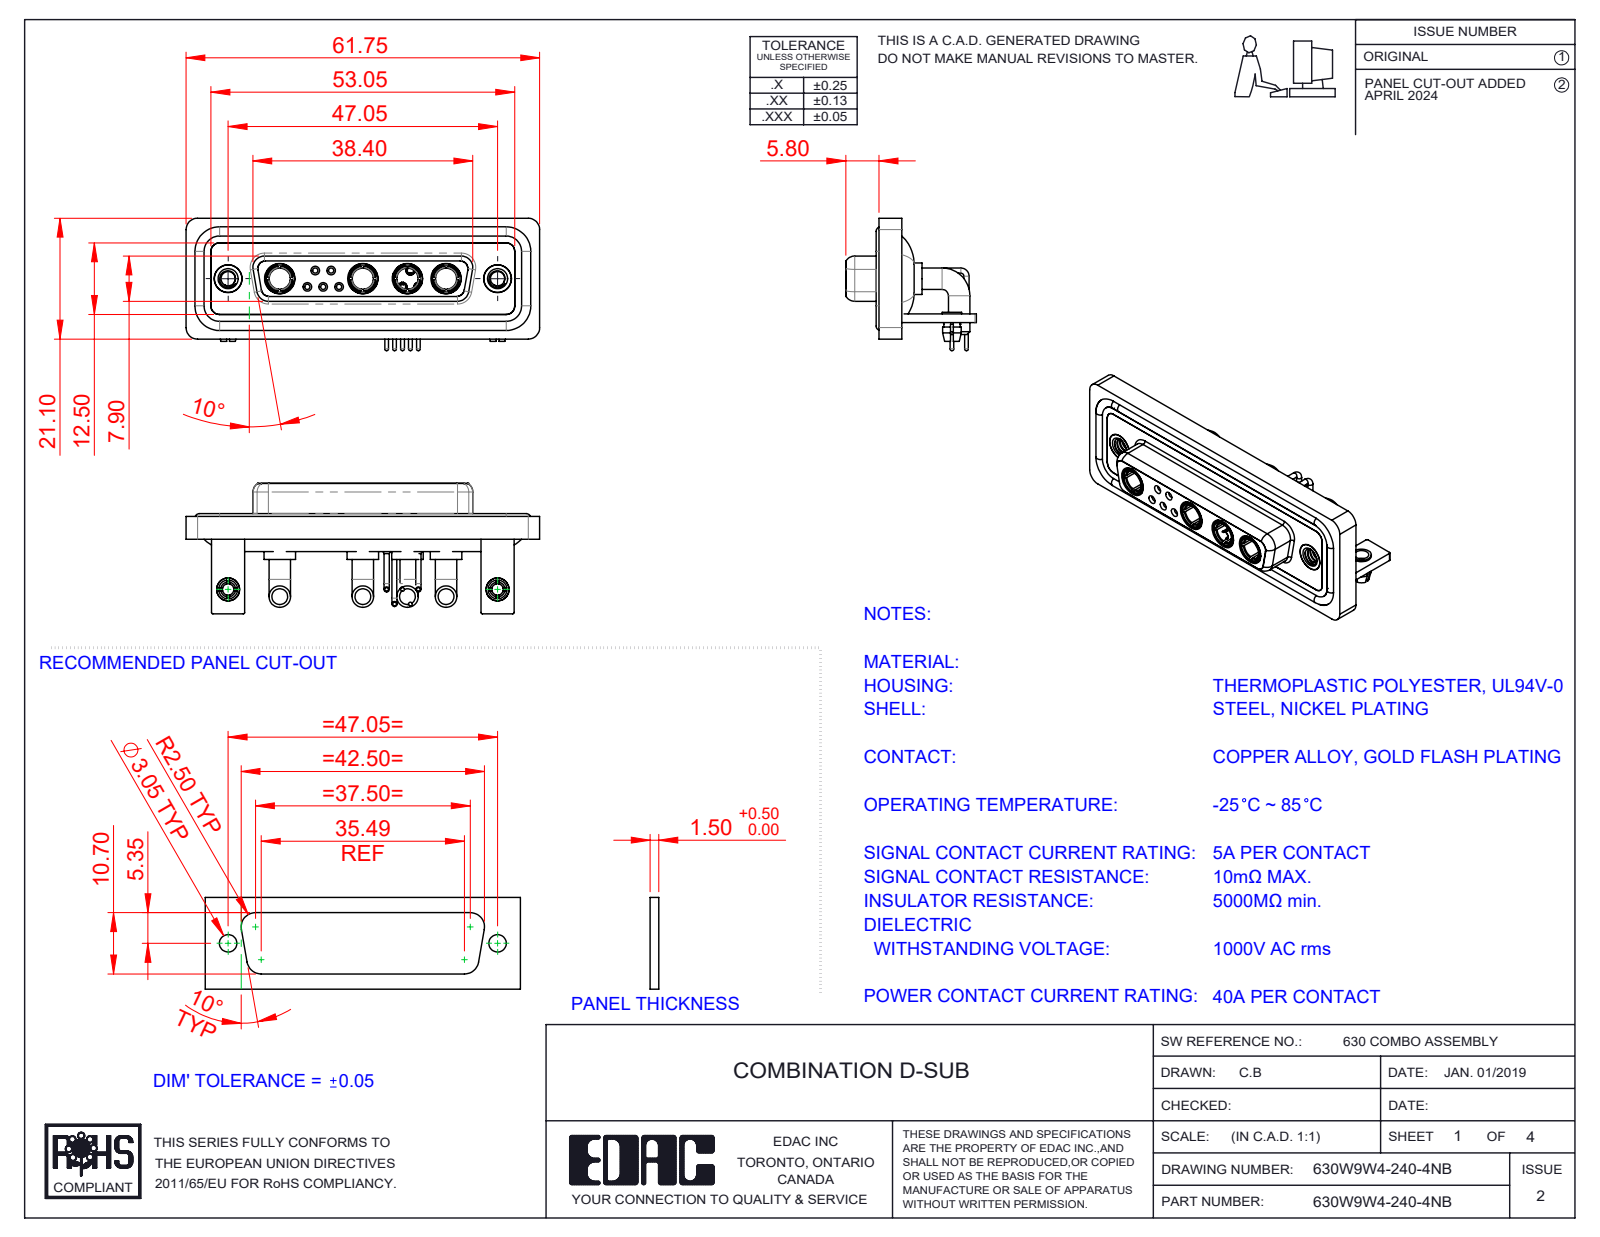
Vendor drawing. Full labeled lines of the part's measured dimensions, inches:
Part name (STEP PRODUCT): 630Combo Waterproof Housing_25 Contacts; 630W9W4-240-4NB; 630Combo Shell Rear_25 Contacts; 630Combo Contact Row 1_50 Contacts (+7 more)
STEP written by: SolidWorks 2023 (CONFIG_CONTROL_DESIGN)
Units: inches
Bodies: 24 solids, 1097 faces (364 planar, 457 cylindrical, 276 other)
Overall size (bounding box): 2.431 × 0.91 × 0.898
Volume: 0.558 in³ · Surface area: 23.52 in²
Round holes (diameter × count): ⌀0.079 ×7, ⌀0.191 ×6, ⌀0.035 ×5, ⌀0.043 ×5, ⌀0.059 ×5, ⌀0.098 ×4, ⌀0.146 ×4, ⌀0.209 ×4, ⌀0.063 ×3, ⌀0.067 ×2, ⌀0.126 ×2, ⌀0.157 ×2
Round bosses / shafts (diameter × count): ⌀0.035 ×10, ⌀0.063 ×9, ⌀0.148 ×8, ⌀0.079 ×5, ⌀0.059 ×5, ⌀0.026 ×5, ⌀0.217 ×4, ⌀0.205 ×4
Partial cylindrical surfaces — rounded edges, fillets, slot ends (radius × count): R0.079 ×19, R0.059 ×18, R0.01 ×16, R0.053 ×8, R0.063 ×8, R0.02 ×5, R0.024 ×4, R0.026 ×4
Main face-to-face distances: 0.016, 0.071, 0.114, 0.146, 0.059, 0.161, 0.043, 0.055, 0.063, 0.098
Hole centre spacings: 0.124, 0.109, 0.198, 0.545, 0.436, 0.504, 0.61, 0.218
